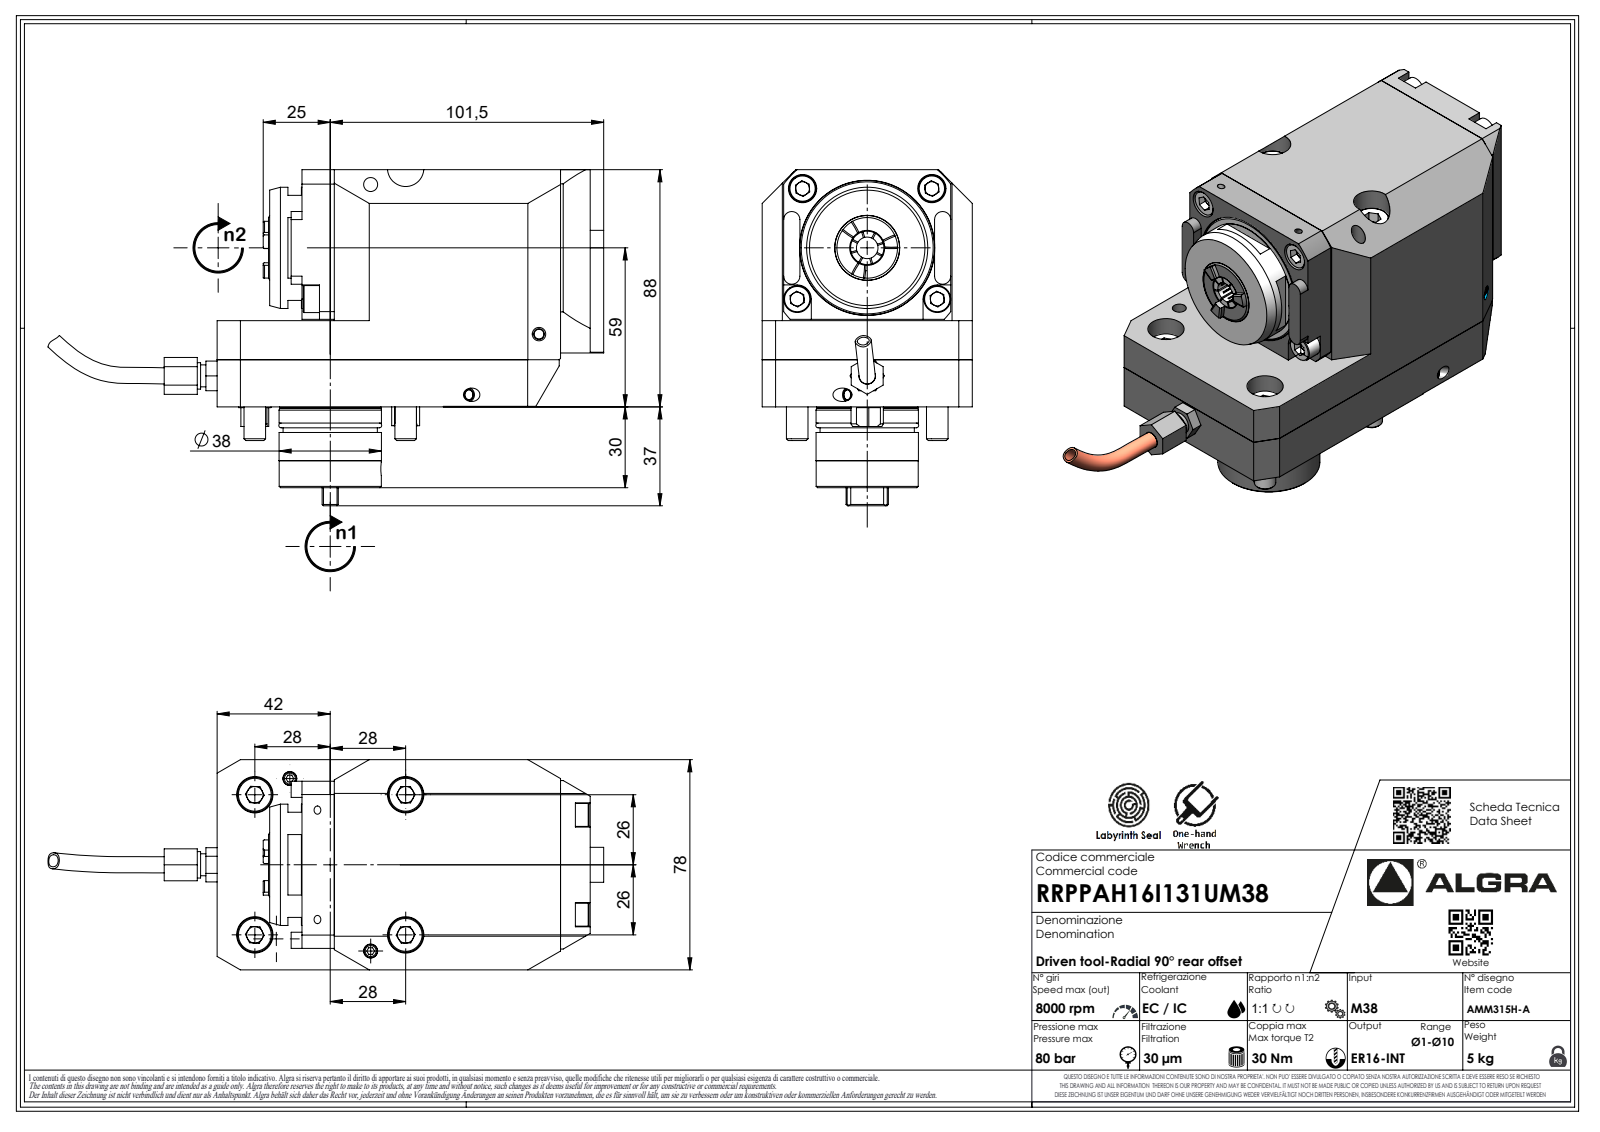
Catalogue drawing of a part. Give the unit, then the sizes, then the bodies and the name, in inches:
Units: inches
Overall size (bounding box): 8.122 × 4.909 × 3.071
Round holes (diameter × count): ⌀0.083 ×1
Round bosses / shafts (diameter × count): ⌀0.315 ×4, ⌀1.772 ×1, ⌀1.496 ×1, ⌀1.492 ×1, ⌀1.48 ×1, ⌀1.378 ×1, ⌀0.472 ×1, ⌀0.386 ×1
Partial cylindrical surfaces — rounded edges, fillets, slot ends (radius × count): R0.013 ×7, R0.02 ×7, R0.146 ×7, R0.118 ×4, R0.008 ×1, R0.236 ×1, R0.256 ×1, R0.309 ×1
Main face-to-face distances: 3.071, 3.465, 2.205, 1.26, 1.252, 3.457, 5.453, 0.768, 0.472, 1.24
Volume: 48.72 in³ · Surface area: 97.55 in²
Bodies: 1 solid, 505 faces (340 planar, 58 cylindrical, 107 other)
Part name (STEP PRODUCT): RRPPAH16I131UM38
STEP written by: SolidWorks 2023 (AUTOMOTIVE_DESIGN)
